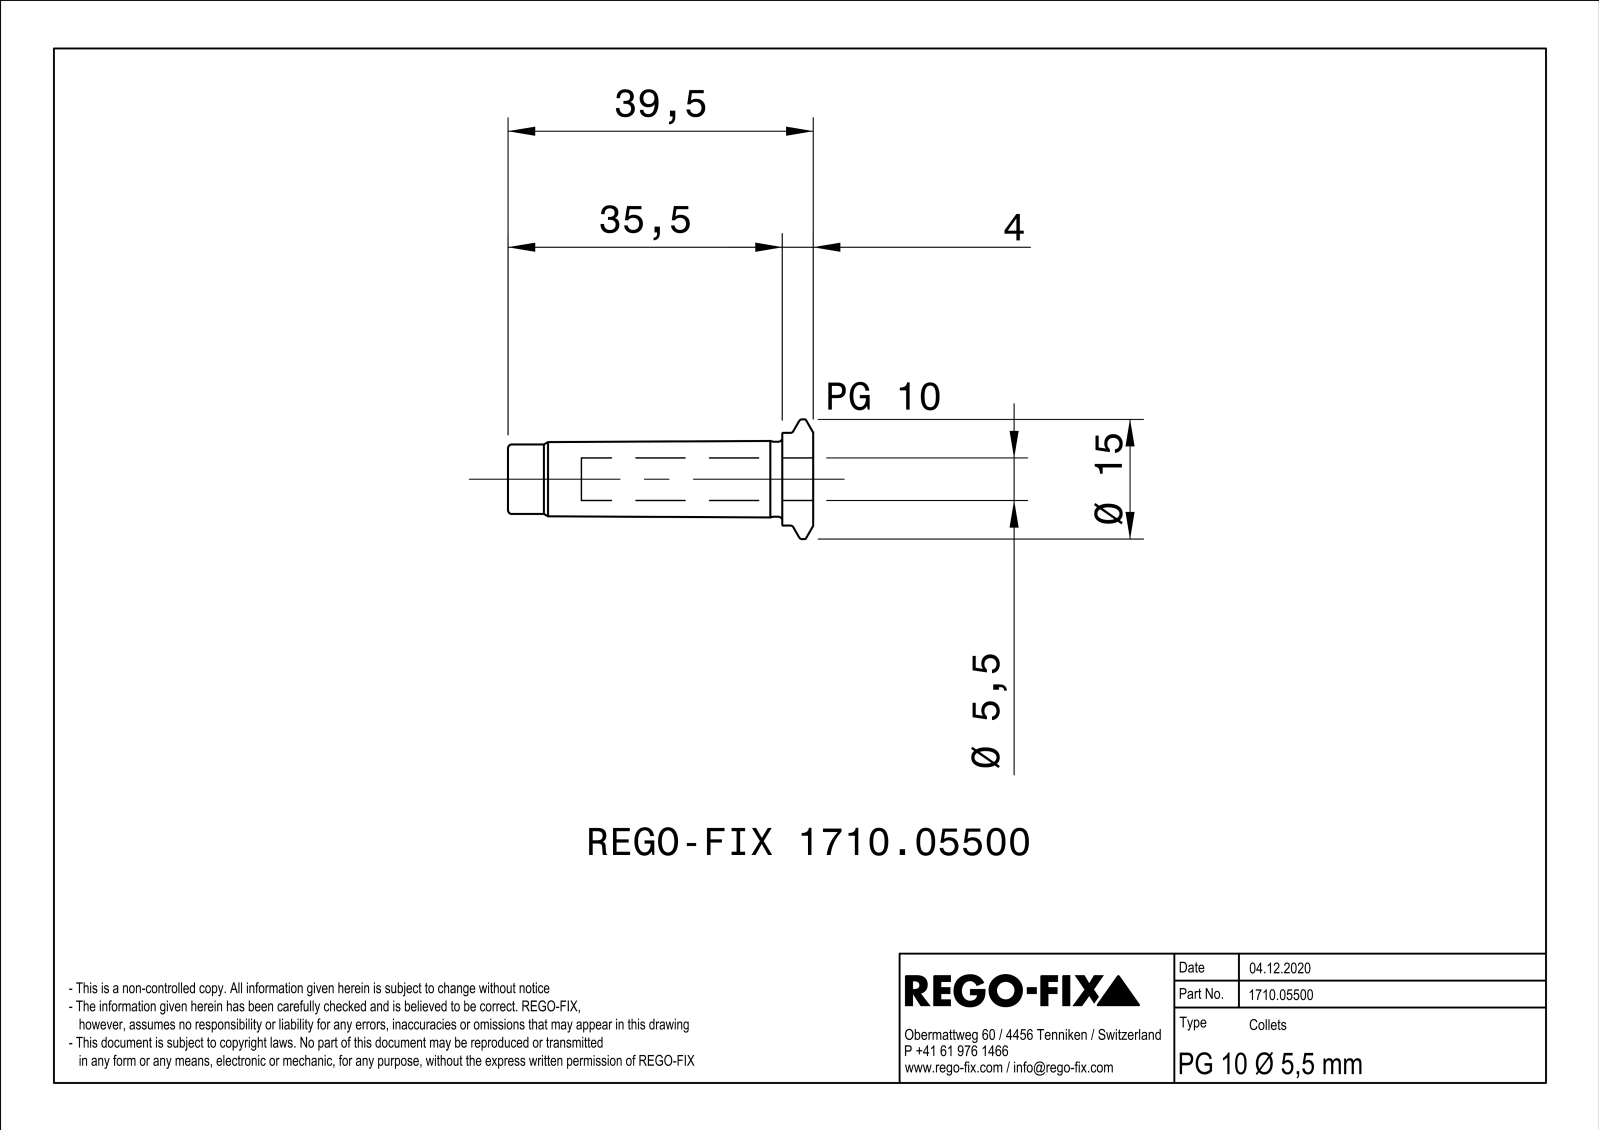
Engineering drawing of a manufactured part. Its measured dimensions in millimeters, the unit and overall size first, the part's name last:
Units: millimetres
Overall size (bounding box): 39.5 × 15.5 × 15.49
Round holes (diameter × count): ⌀5.5 ×1, ⌀6.19 ×1
Round bosses / shafts (diameter × count): ⌀15.5 ×1, ⌀12 ×1, ⌀9.7 ×1, ⌀9 ×1
Partial cylindrical surfaces — rounded edges, fillets, slot ends (radius × count): R0.4 ×6
Main face-to-face distances: 0.8, 39.5, 4, 35.5
Bodies: 0 solids, 58 faces (11 planar, 18 cylindrical, 29 other)
Part name (STEP PRODUCT): NOCUT
STEP written by: SIEMENS PLM Software Solid Edge ST10 (AUTOMOTIVE_DESIGN)
